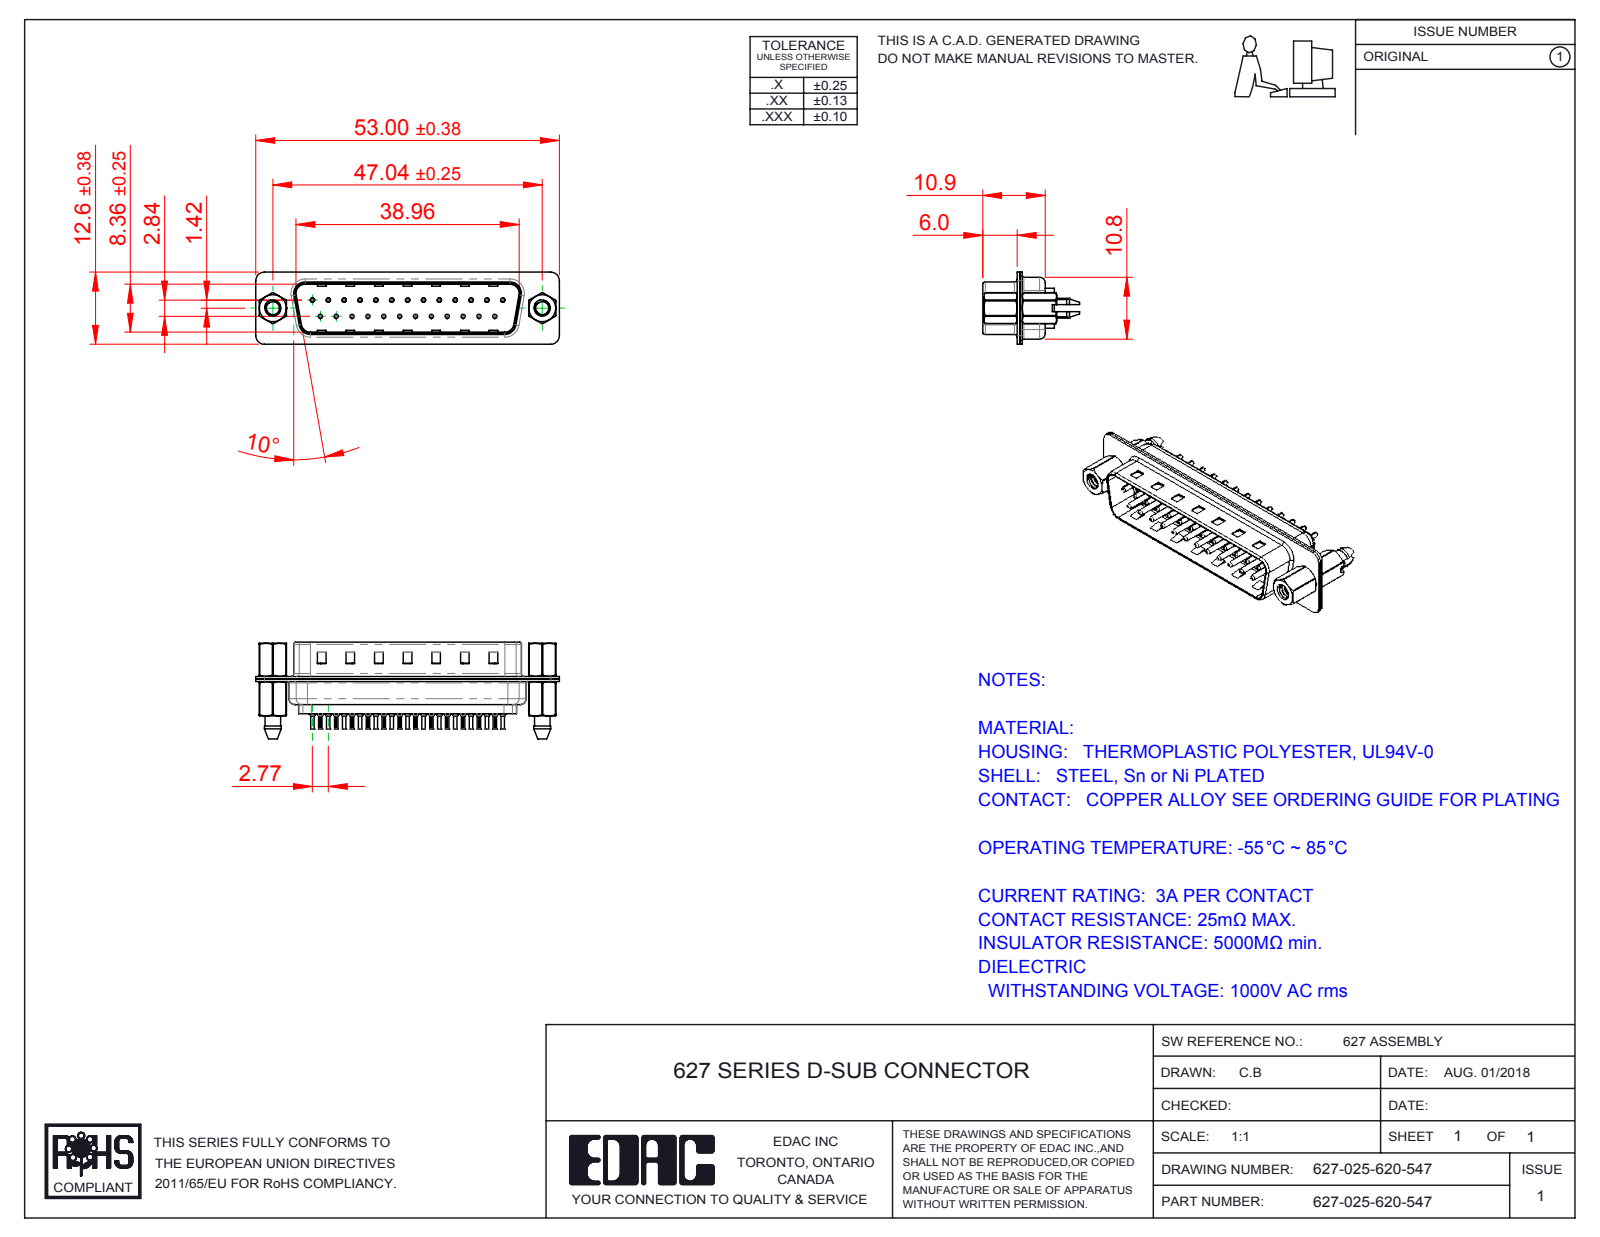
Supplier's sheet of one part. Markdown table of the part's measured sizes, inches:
| quantity | value |
| --- | --- |
| part name | 627 Contact Row 2_20L; 627 Housing_25 LP; 627 Shell Front_25 Contacts; 627 Shell Rear_25 Contacts (+4 more) |
| STEP written by | SolidWorks 2016 (CONFIG_CONTROL_DESIGN) |
| units | inches |
| bodies | 32 solids, 3026 faces (825 planar, 1166 cylindrical, 1035 other) |
| overall size | 2.087 × 0.665 × 0.496 |
| volume | 0.183 in³ |
| surface area | 13.06 in² |
| round holes (diameter × count) | 0.008 × 25, 0.014 × 25, 0.043 × 25, 0.063 × 25, 0.089 × 2, 0.09 × 2, 0.157 × 2, 0.189 × 2 |
| round bosses / shafts (diameter × count) | 0.079 × 25, 0.059 × 25, 0.03 × 25, 0.024 × 25, 0.193 × 2, 0.11 × 2 |
| partial cylindrical surfaces (radius × count) | 0.004 × 50, 0.059 × 18, 0.079 × 12, 0.063 × 10, 0.02 × 8, 0.01 × 4, 0.024 × 4, 0.026 × 4 |
| main face-to-face distances | 0.016, 0.018, 0.032, 0.377, 0.345, 0.035, 0.059, 0.055, 0.256, 0.238 |
| hole center spacings | 0.124, 0.327, 0.109, 0.218, 0.436, 0.654, 0.198, 0.198 |
